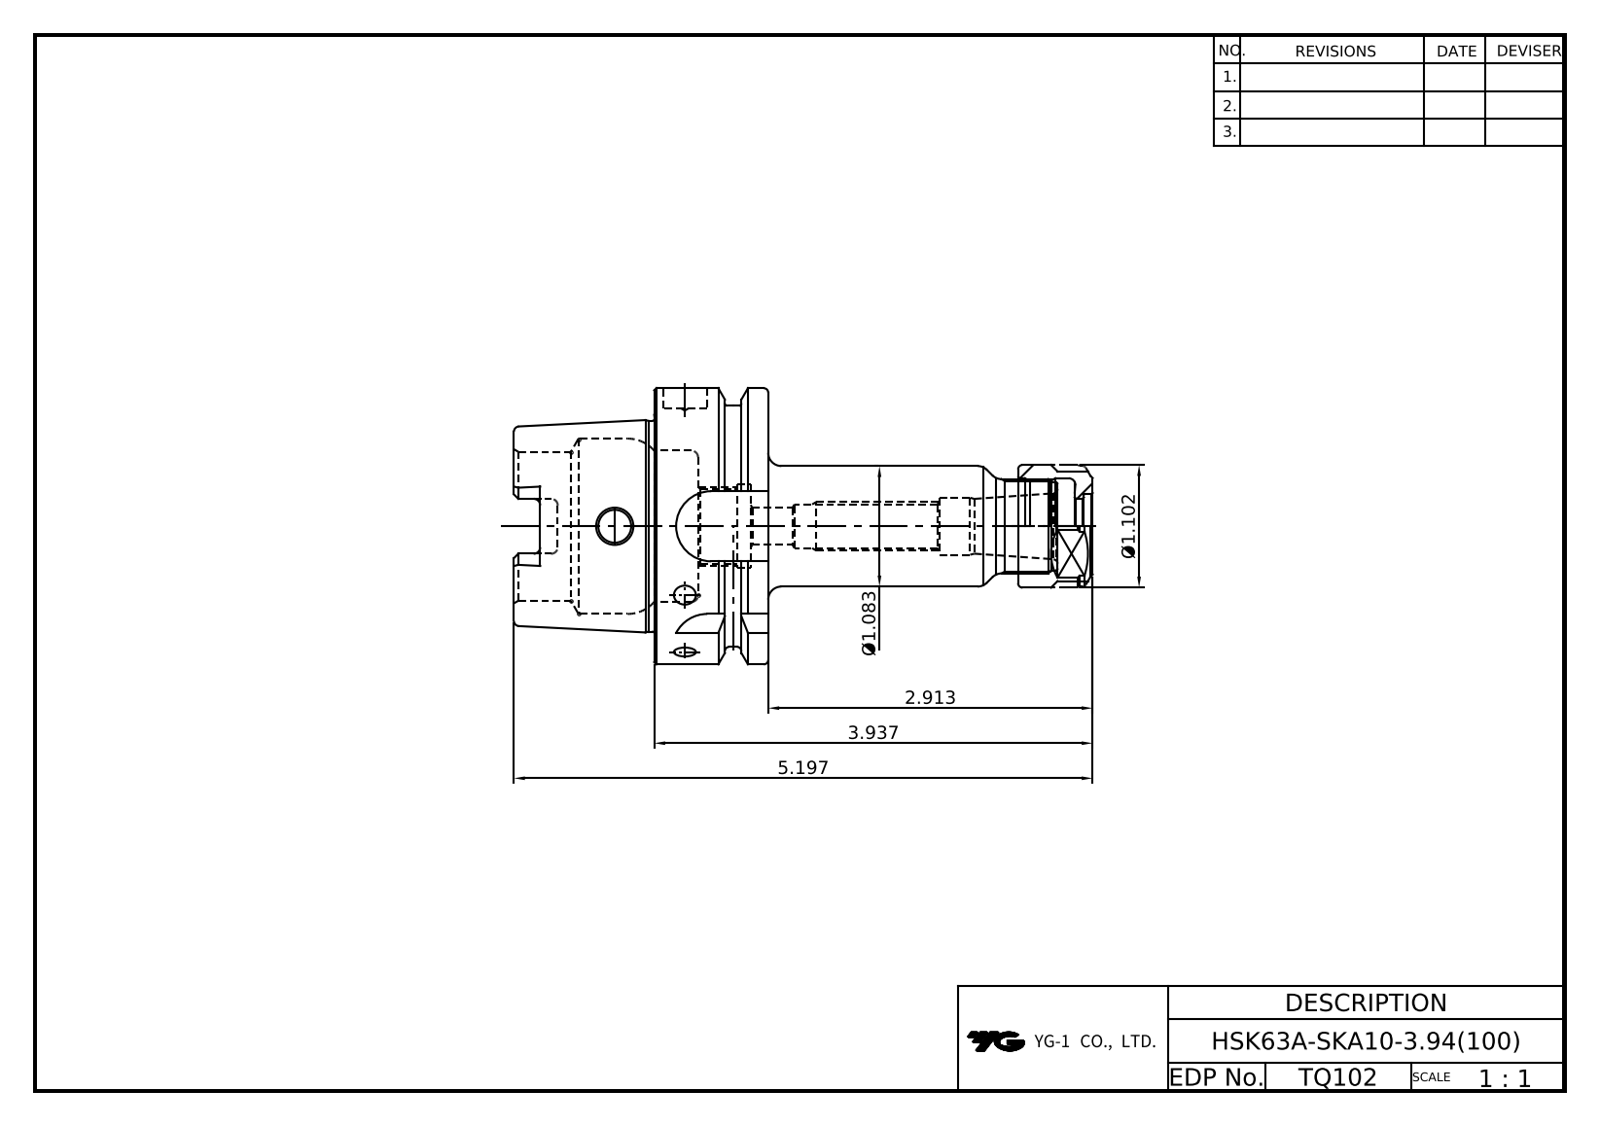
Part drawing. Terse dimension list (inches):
name: LO-HSK63A-SKA10-100; SKN10-NUT
written by: Autodesk Inventor 2024 (AUTOMOTIVE_DESIGN)
unit: in
bodies: 2 solids, 172 faces (57 planar, 47 cylindrical, 68 other)
size: 5.197 × 2.48 × 2.48
volume: 7.016 in³; area: 50.97 in²
holes: 1× ⌀0.295, 1× ⌀0.315, 1× ⌀0.37, 1× ⌀0.394, 1× ⌀0.496, 1× ⌀0.512, 1× ⌀0.575, 1× ⌀0.666, 1× ⌀0.748, 1× ⌀0.846, 1× ⌀0.862, 1× ⌀1.339
bosses: 1× ⌀2.48, 1× ⌀2.165, 1× ⌀1.891, 1× ⌀1.102, 1× ⌀1.083, 1× ⌀0.795
rounds: 6× R0.059, 4× R0.113, 4× R0.315, 1× R0.543
face distances: 1.024, 0.394, 0.63, 1.26, 1.654, 2.283, 2.087, 0.866, 0.157, 0.472
